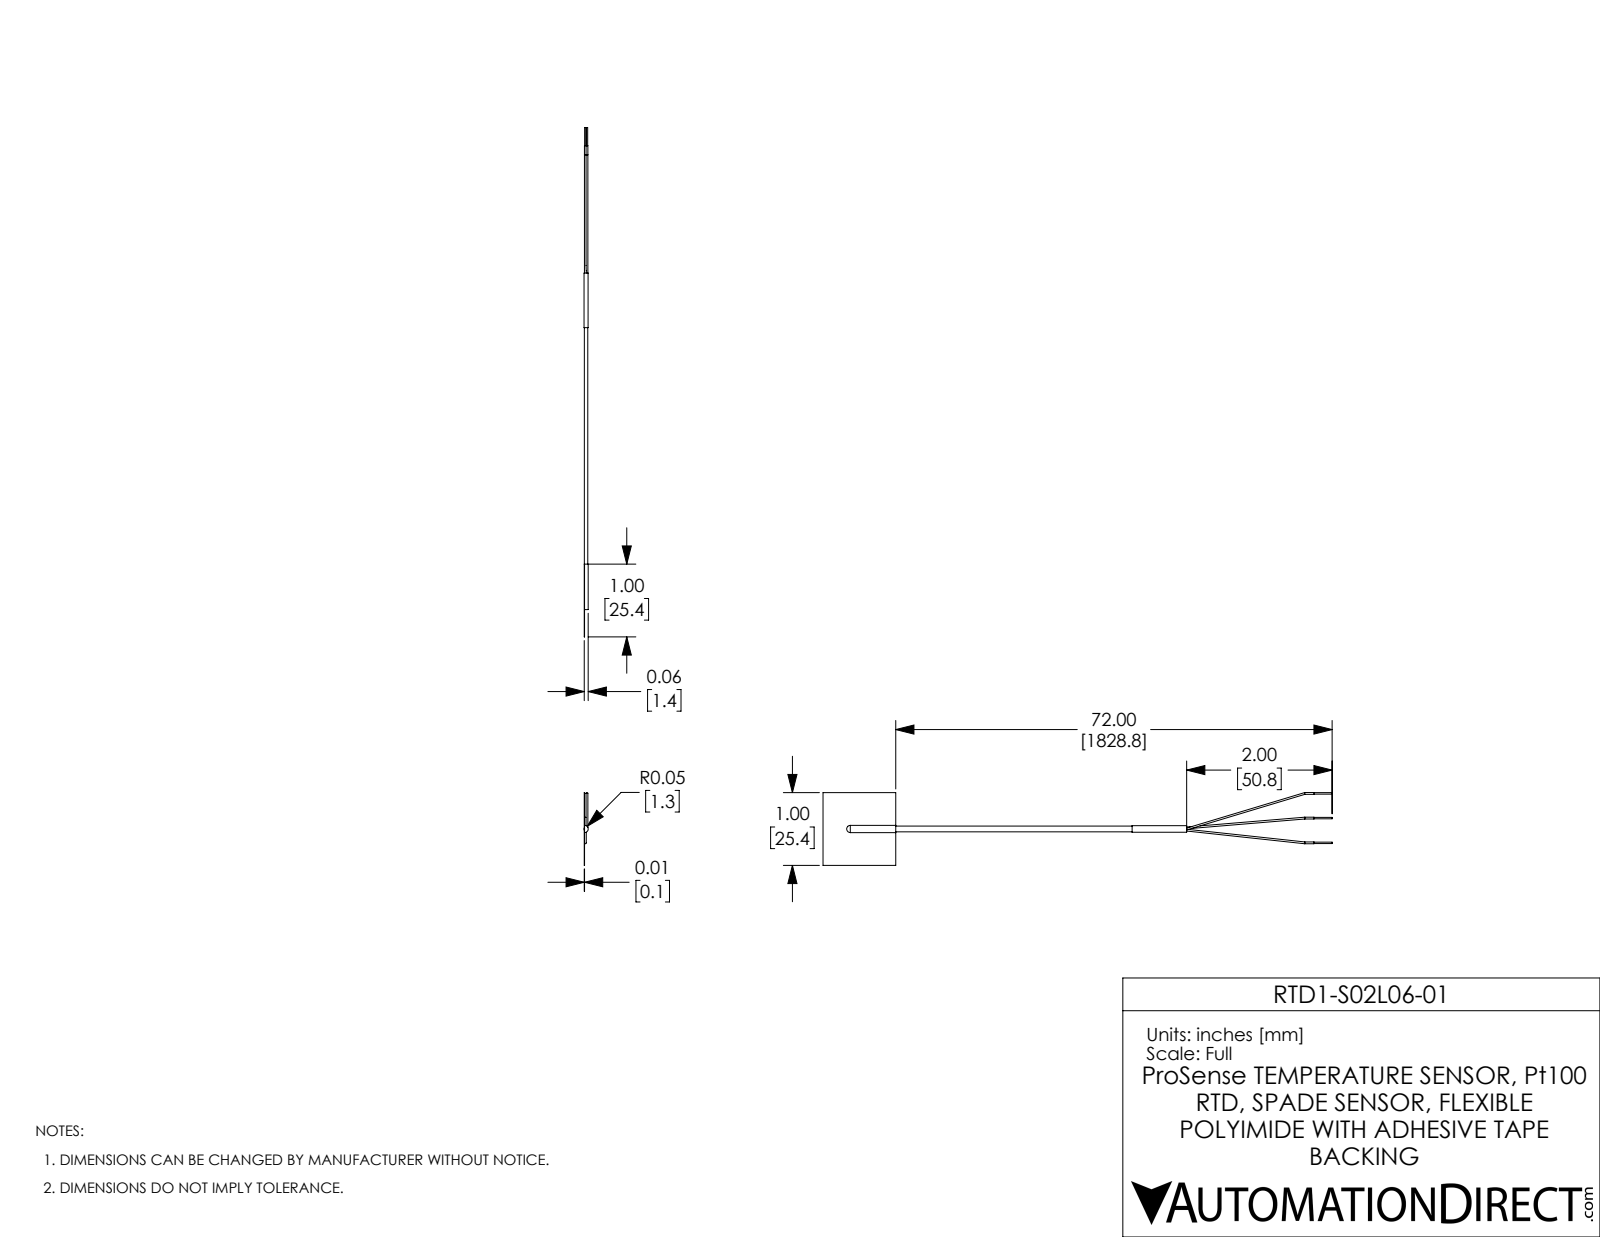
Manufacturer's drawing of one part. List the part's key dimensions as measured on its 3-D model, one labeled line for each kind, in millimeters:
Part name (STEP PRODUCT): RTD1-S02L06-01
STEP written by: SolidWorks 2017 (AUTOMOTIVE_DESIGN)
Units: millimetres
Bodies: 3 solids, 48 faces (17 planar, 20 cylindrical, 11 other)
Overall size (bounding box): 177.8 × 25.4 × 1.4
Volume: 390 mm³ · Surface area: 2 248 mm²
Round bosses / shafts (diameter × count): ⌀0.6 ×6, ⌀0.5 ×3
Partial cylindrical surfaces — rounded edges, fillets, slot ends (radius × count): R1.3 ×1
Main face-to-face distances: 25.4, 101.6, 127, 6.4, 12.7, 88.9, 114.3, 63.5, 19.1, 82.6
